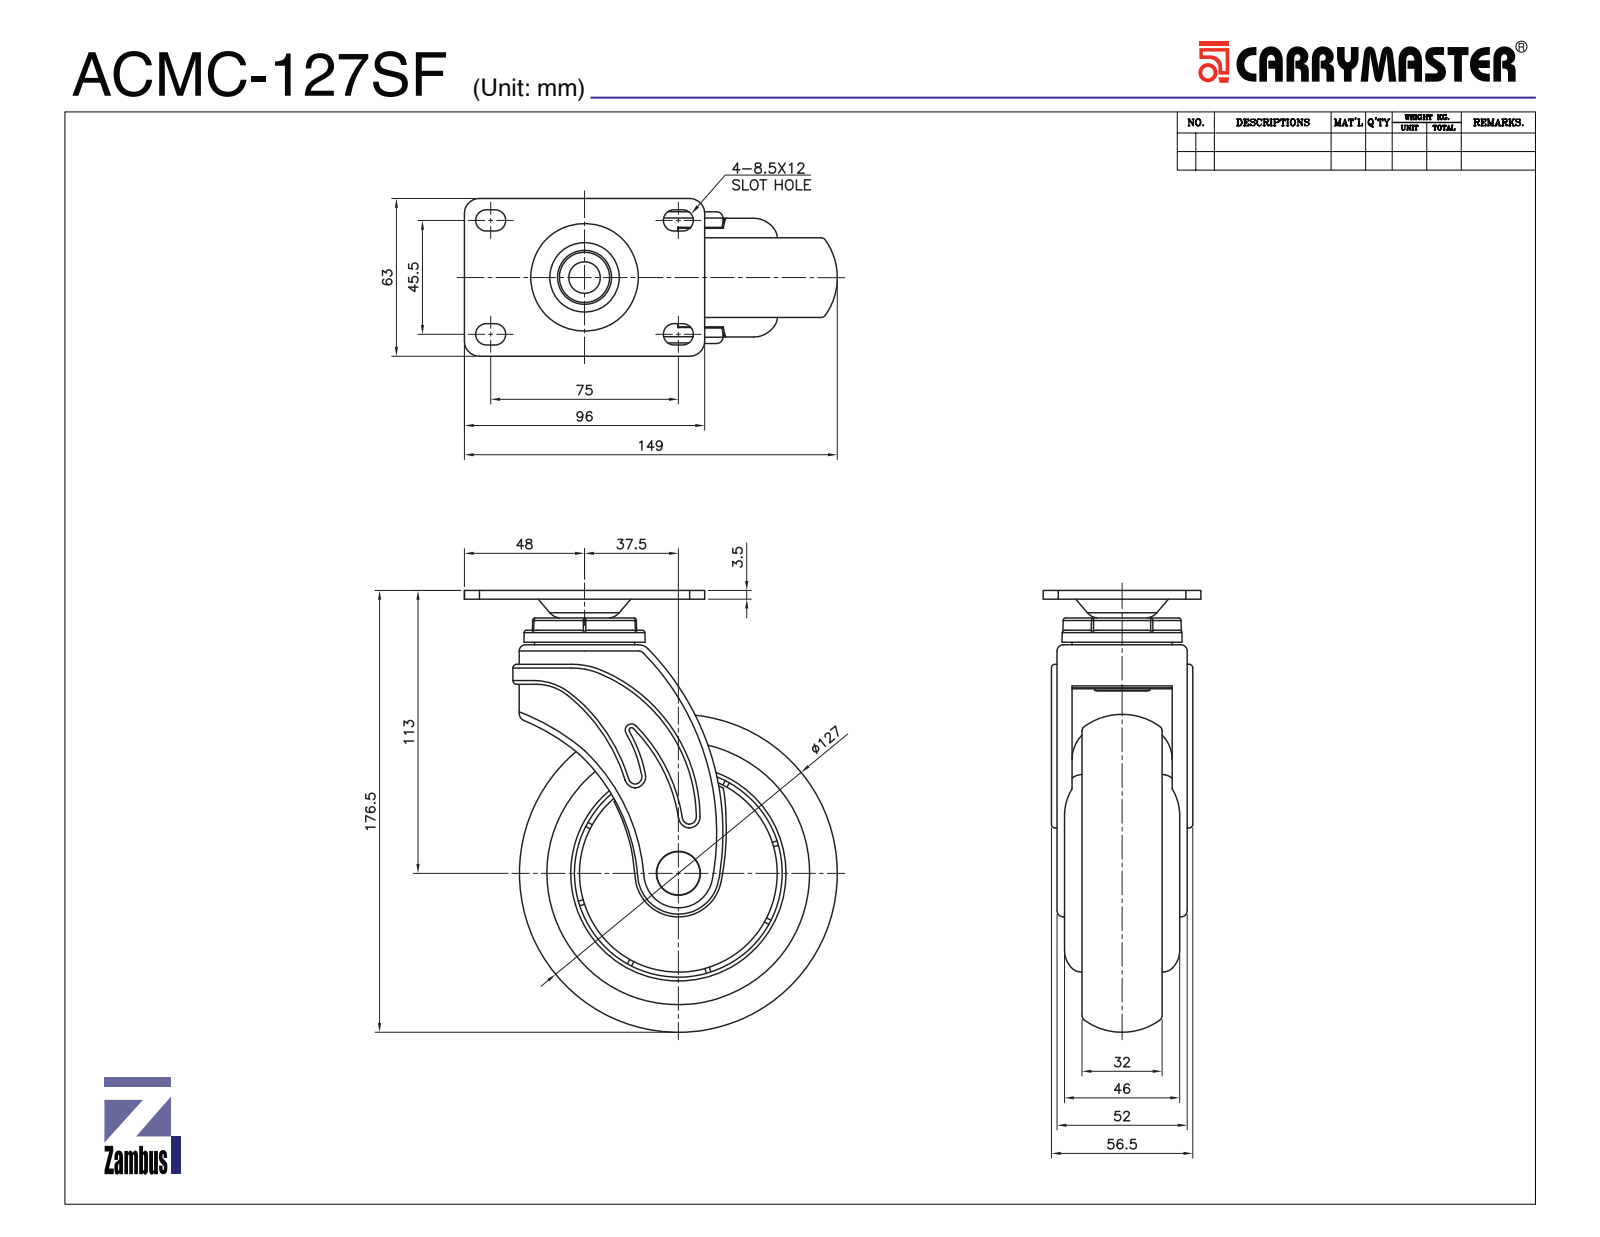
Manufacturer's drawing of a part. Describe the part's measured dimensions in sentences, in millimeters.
The part is named "ACMC-127 TOP PLATE COVER; ACMC-127 NON BRAKE FRAME; ACMC-127SF; ACMC-127 F TOP PLATE (+1 more)". Its 3-D file was written by "SolidWorks 2019 (CONFIG_CONTROL_DESIGN)". It is 4 solids with 283 faces: 78 planar, 109 cylindrical and 96 other. Overall it measures 176.5 by 149 by 63 millimeters. Its volume is 564 205 cubic millimeters and its surface area 93 431 square millimeters. Round holes: 1 of diameter 17.3, 1 of diameter 37, 1 of diameter 83, 1 of diameter 105.01. Round bosses or shafts: 1 of diameter 105, 1 of diameter 79, 1 of diameter 78.59, 1 of diameter 40, 1 of diameter 25, 1 of diameter 22, 1 of diameter 17. Partial cylindrical surfaces (rounded edges, fillets, slot ends): 13 of radius 1, 8 of radius 4.25, 4 of radius 4.5, 4 of radius 6, 2 of radius 2.5, 1 of radius 5, 1 of radius 16.3, 1 of radius 16.8. The main face-to-face distances are 4.25, 36.25, 6, 32, 10.25, 42.25, 46.5, 3.5, 40.5, 6.25.
